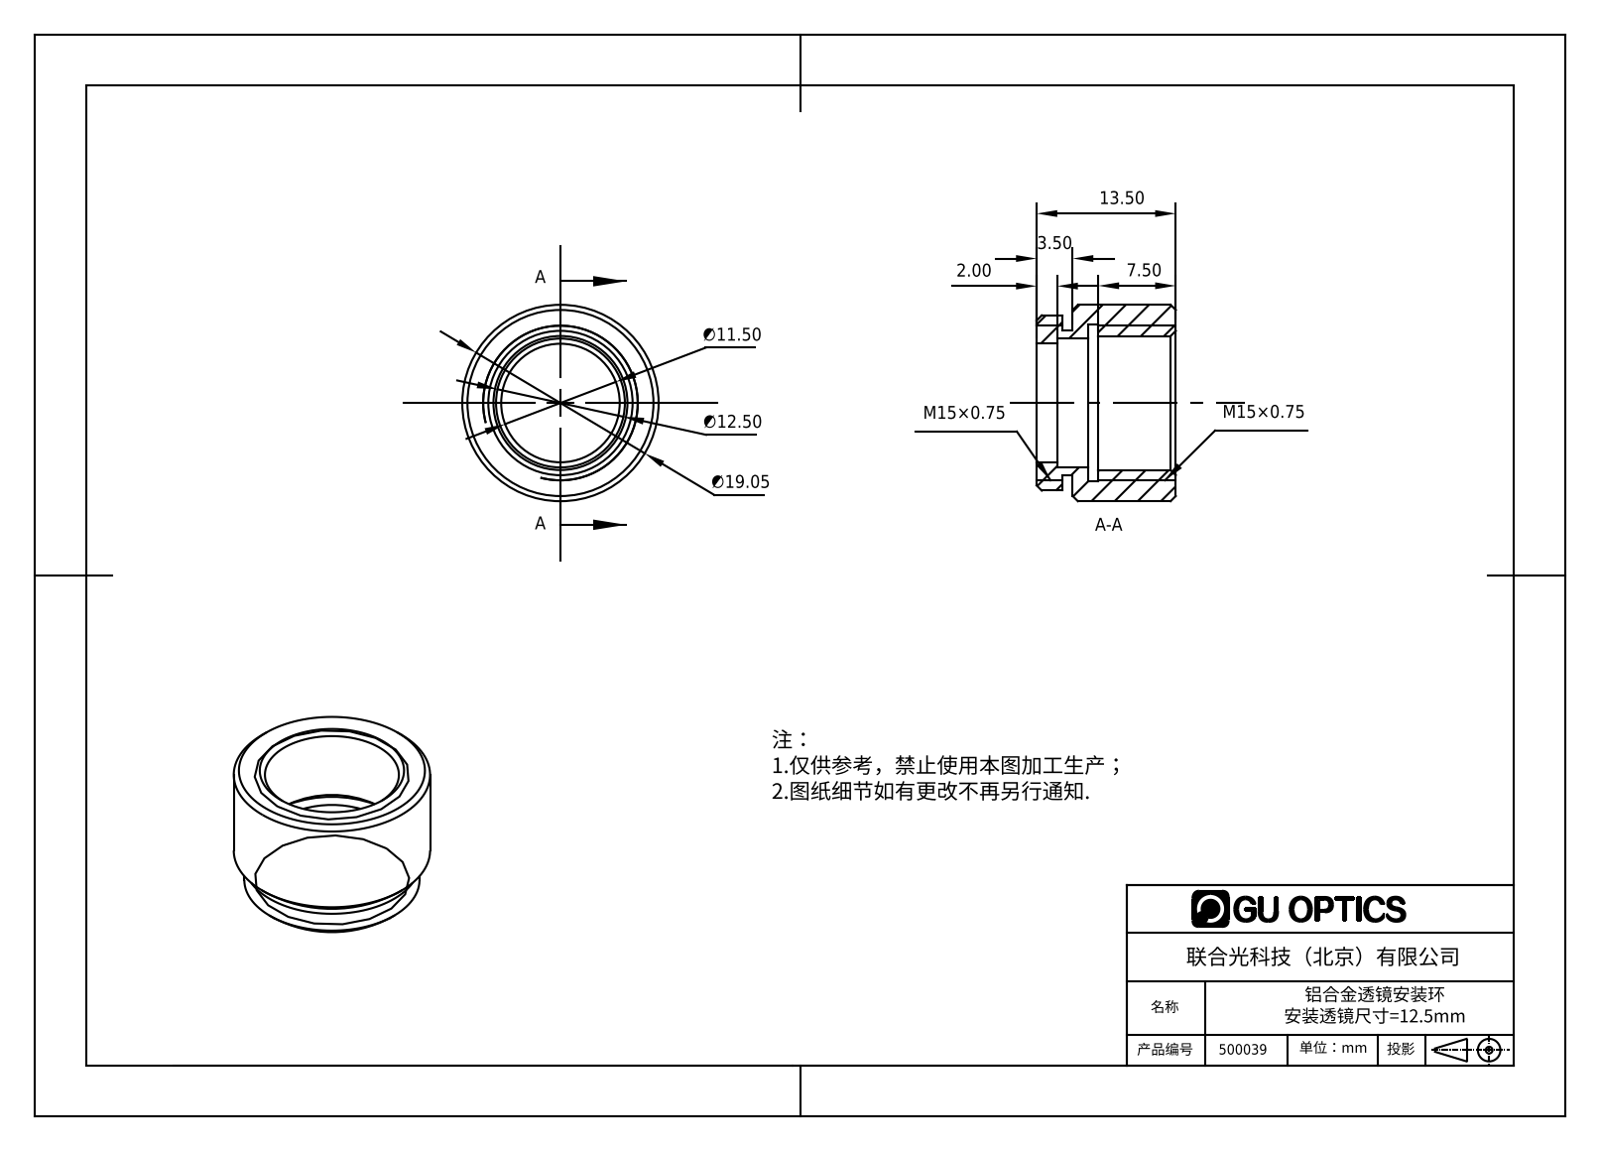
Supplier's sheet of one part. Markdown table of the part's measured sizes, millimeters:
| quantity | value |
| --- | --- |
| part name | 500039 |
| STEP written by | SolidWorks 2016 (AUTOMOTIVE_DESIGN) |
| units | millimeters |
| bodies | 1 solid, 29 faces (7 planar, 14 cylindrical, 8 other) |
| overall size | 19.05 × 19.05 × 13.5 |
| volume | 1 792 mm³ |
| surface area | 1 863 mm² |
| round holes (diameter × count) | 11.5 × 1, 12.5 × 1, 13 × 1, 15.2 × 1 |
| round bosses / shafts (diameter × count) | 19.05 × 1, 17 × 1, 14 × 1 |
| main face-to-face distances | 2.5, 3.5, 1, 10, 13.5, 1.5, 11, 5, 8.5, 6 |
